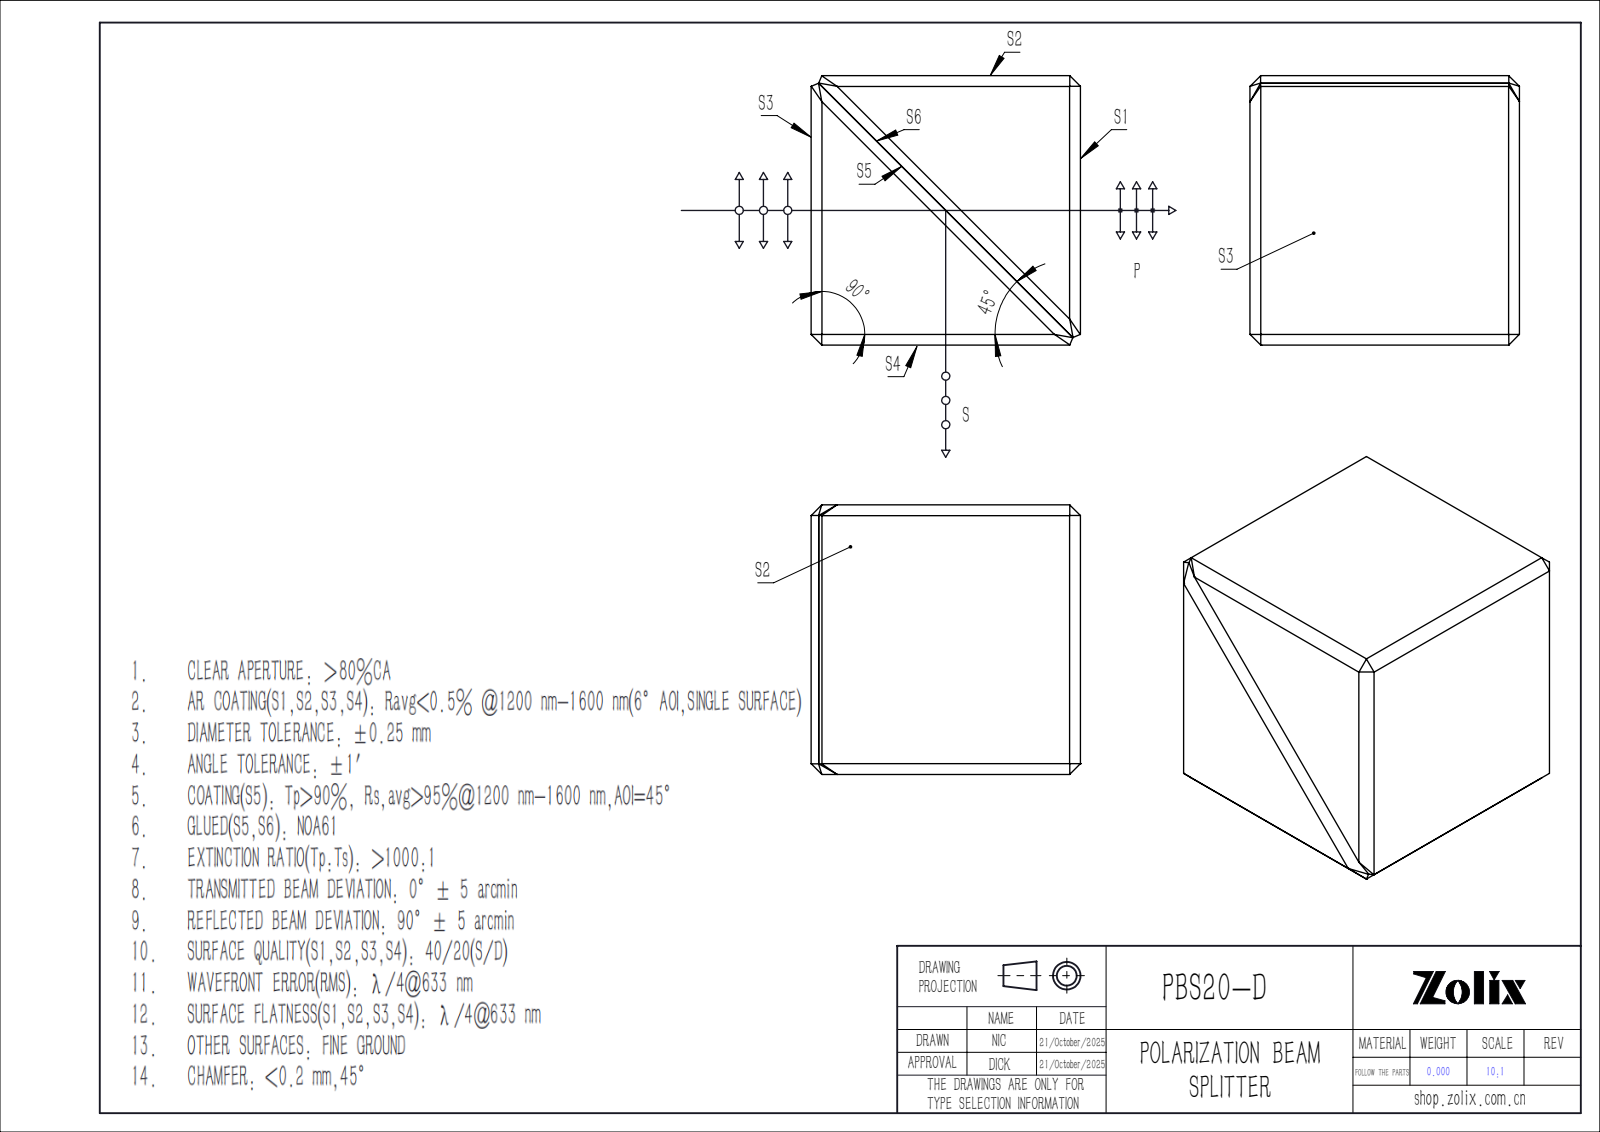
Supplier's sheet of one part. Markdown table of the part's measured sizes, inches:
| quantity | value |
| --- | --- |
| part name | PBS634-1-1; PBS634-1-2; PBS634 |
| STEP written by | SolidWorks 2022 (CONFIG_CONTROL_DESIGN) |
| units | inches |
| bodies | 2 solids, 43 faces (41 planar, 2 cylindrical, 0 other) |
| overall size | 0.787 × 0.787 × 0.787 |
| volume | 0.488 in³ |
| surface area | 5.388 in² |
| round holes (diameter × count) | 0.016 × 1 |
| main face-to-face distances | 0.787, 1.102, 0.546, 1.015, 0.551, 1.102, 0.551, 0.031, 0.756, 1.178 |
